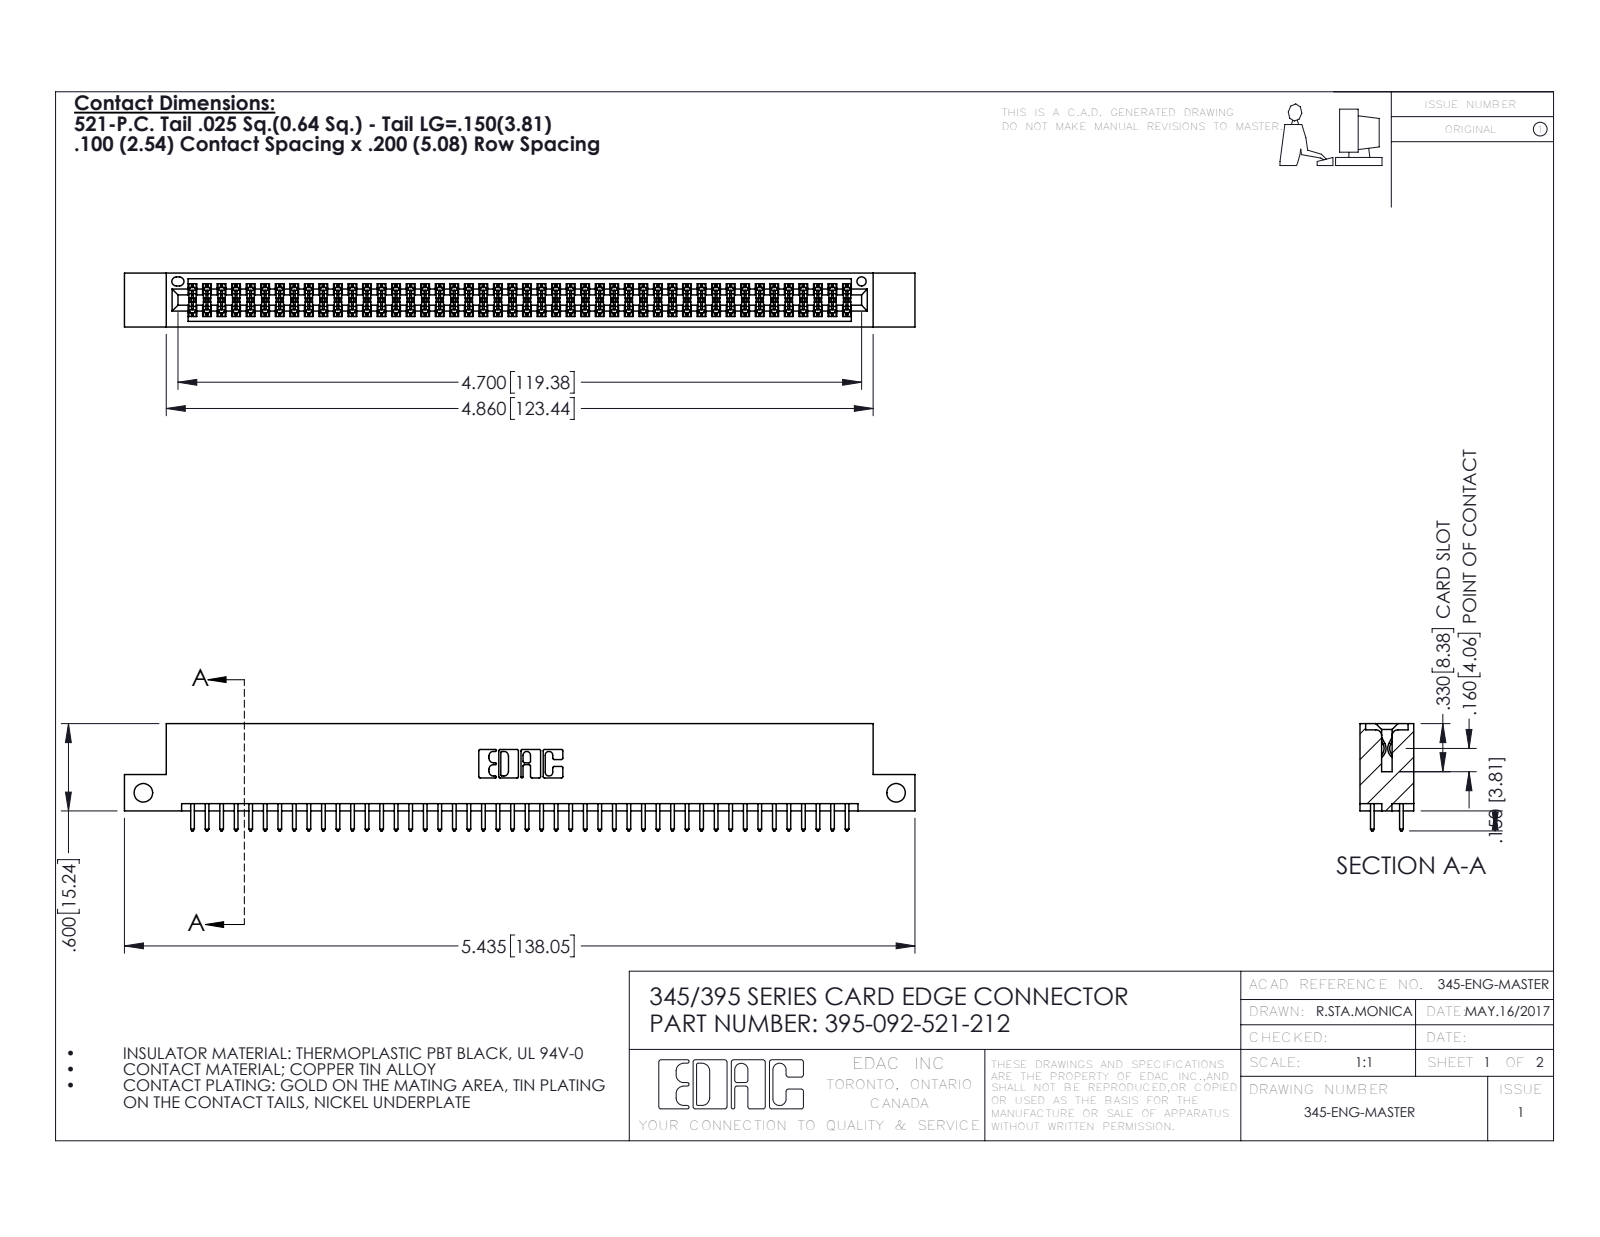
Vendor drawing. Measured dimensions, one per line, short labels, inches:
name: 345 Part_Flush Mounting Lugs - Side Mount; 345-292-001_345-293-121; 395-092-521-212
written by: SolidWorks 2016 (CONFIG_CONTROL_DESIGN)
unit: in
bodies: 93 solids, 4726 faces (3116 planar, 1610 cylindrical, 0 other)
size: 5.435 × 0.737 × 0.37
volume: 0.813 in³; area: 30.06 in²
holes: 2× ⌀0.128, 1× ⌀0.064
rounds: 138× R0.006, 92× R0.01, 22× R0.01, 6× R0.007, 6× R0.031, 3× R0.026, 2× R0.014, 2× R0.019
face distances: 0.298, 0.072, 0.2, 0.37, 0.098, 0.272, 0.025, 0.225, 0.175, 0.149
hole spacings: 5.175
